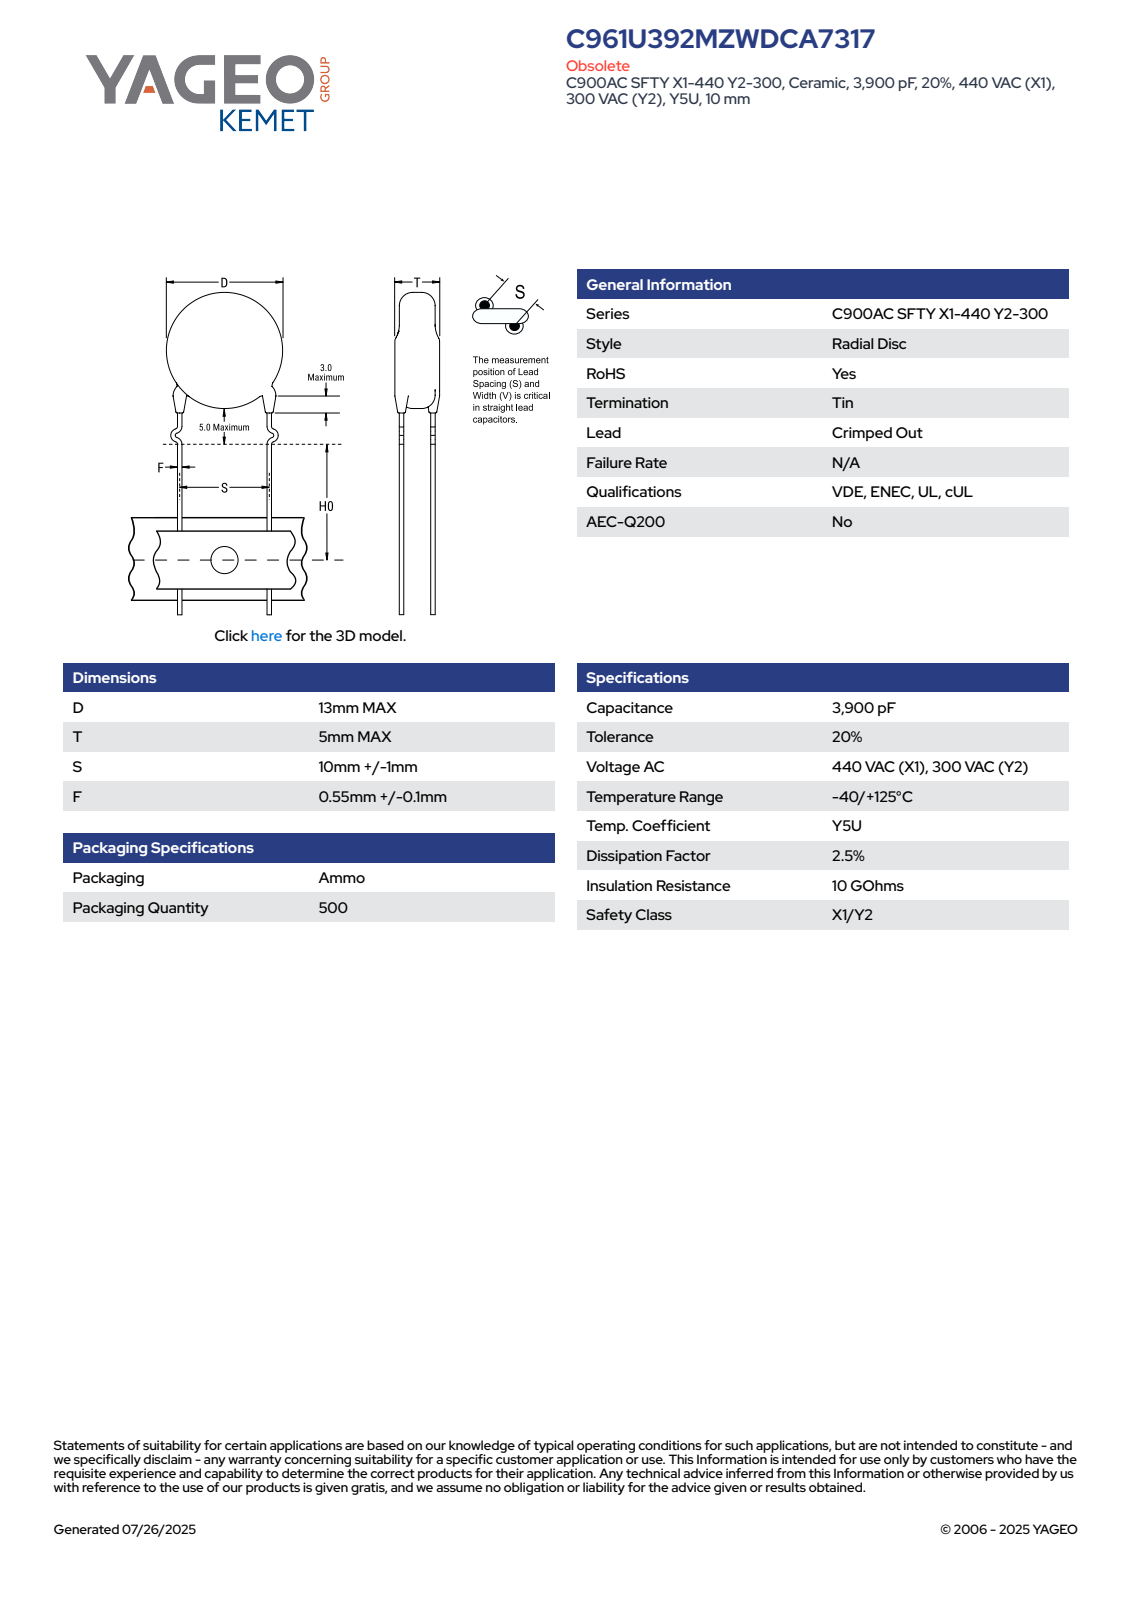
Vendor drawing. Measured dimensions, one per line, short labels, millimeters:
name: CCD_KCOC900_D13T5S10LL20F0.55
written by: SolidWorks 2014 (AUTOMOTIVE_DESIGN)
unit: mm
bodies: 4 solids, 85 faces (63 planar, 6 cylindrical, 16 other)
size: 38 × 15.07 × 5
volume: 670 mm³; area: 573 mm²
bosses: 2× ⌀1.2, 1× ⌀13
face distances: 5, 7.19, 5.84, 1.35, 0.37, 0.33, 1.09, 5.52, 2.79, 4.01
